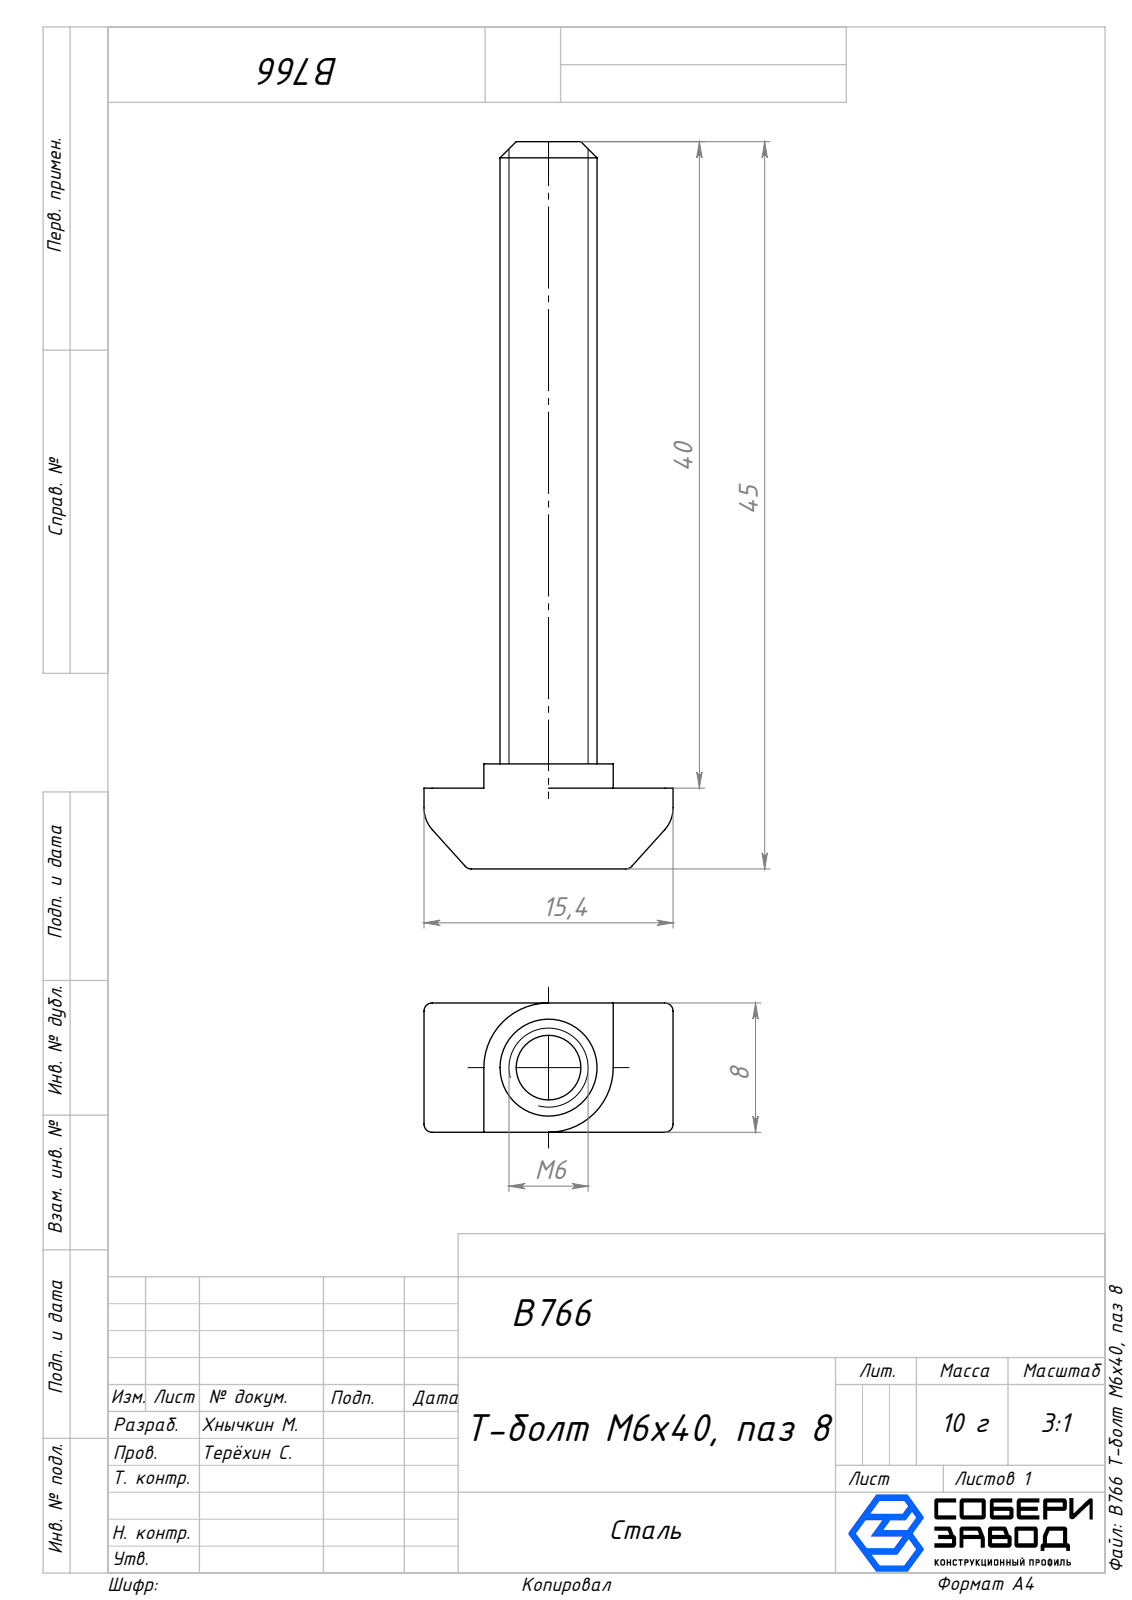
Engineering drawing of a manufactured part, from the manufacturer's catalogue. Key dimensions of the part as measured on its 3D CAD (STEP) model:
Part name (STEP PRODUCT): B766 Т-болт М6х40, паз 8
STEP written by: SolidWorks 2025 (AUTOMOTIVE_DESIGN)
Units: millimetres
Bodies: 1 solid, 41 faces (13 planar, 18 cylindrical, 10 other)
Overall size (bounding box): 45 × 15.4 × 8
Volume: 1 714 mm³ · Surface area: 1 182 mm²
Round bosses / shafts (diameter × count): ⌀6 ×1
Partial cylindrical surfaces — rounded edges, fillets, slot ends (radius × count): R0.5 ×12, R2 ×2, R4 ×1
Main face-to-face distances: 8, 5, 6.5, 1.5, 45, 40, 38.5, 3.7, 11.7, 15.4
